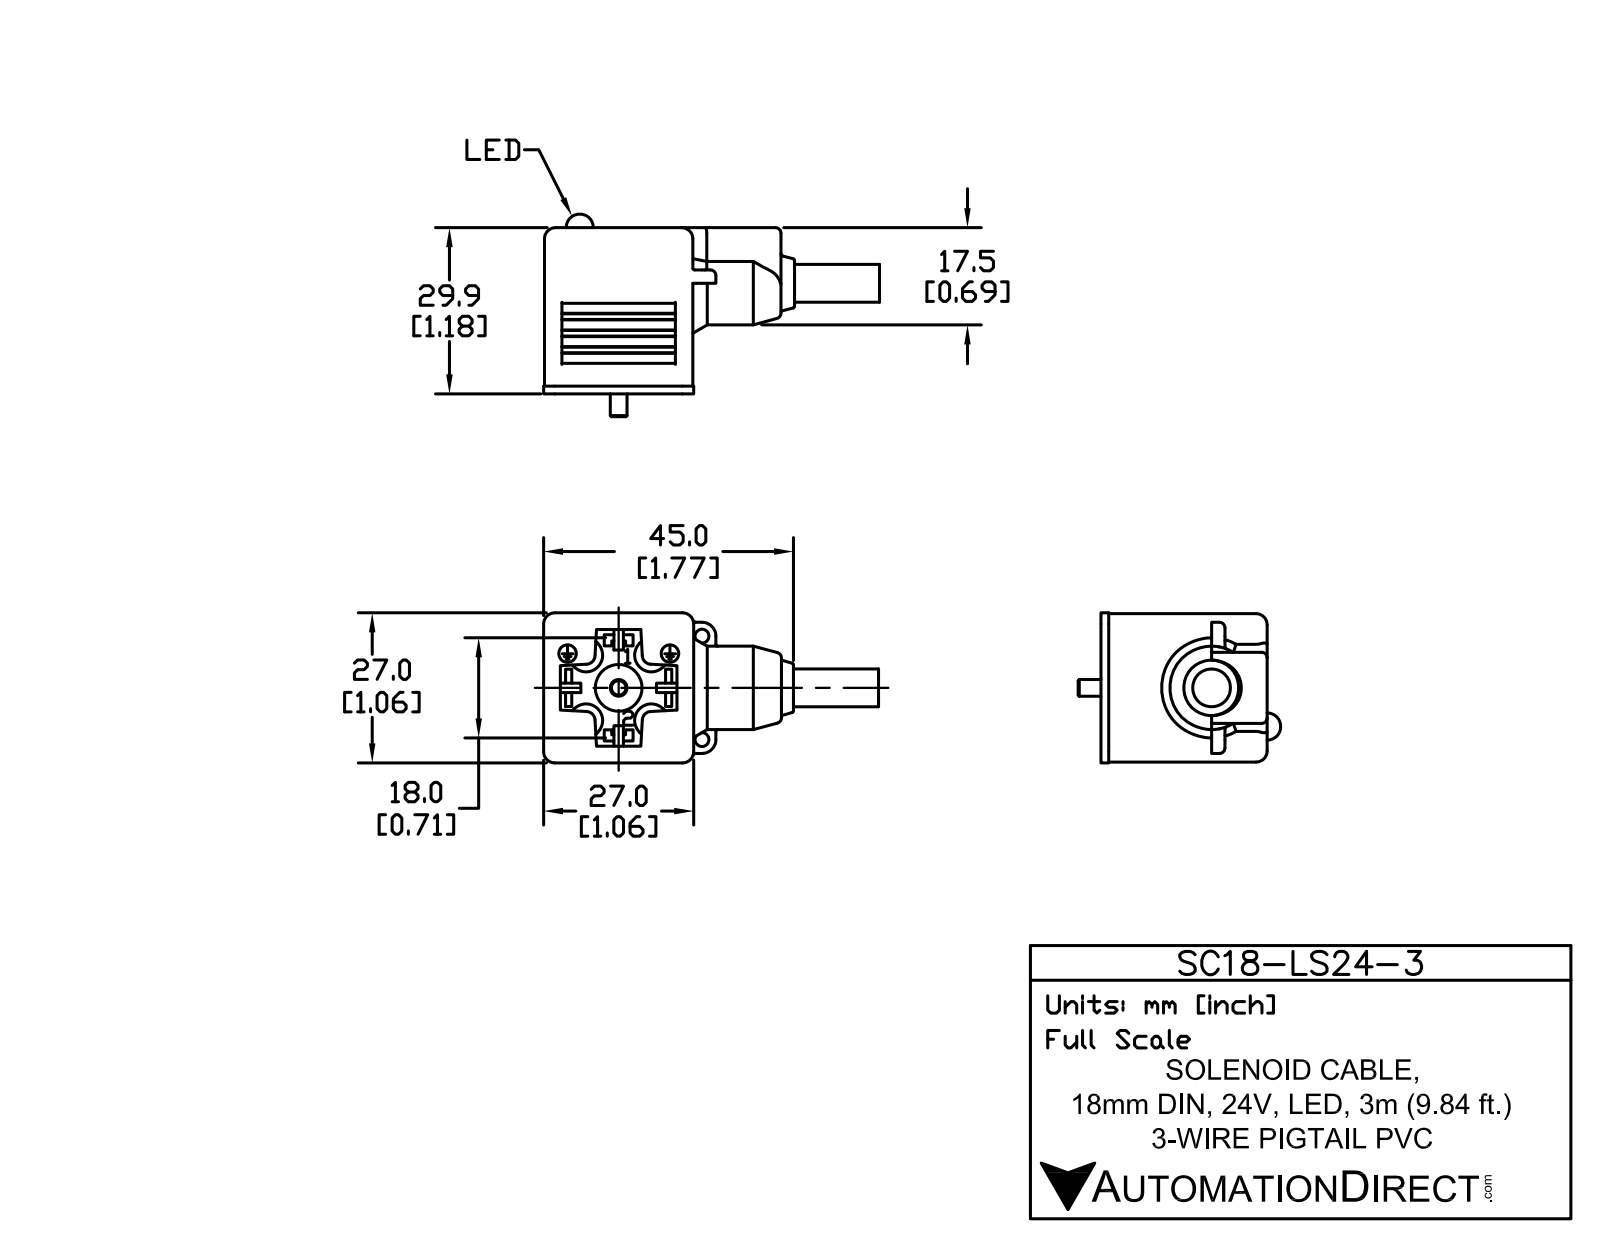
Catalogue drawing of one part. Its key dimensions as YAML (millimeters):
part_name: "SC18-LS24-3"
step_written_by: "SolidWorks 2011 (AUTOMOTIVE_DESIGN)"
units: millimeters
bodies: {solids: 5, faces: 269, planar: 210, cylindrical: 34, other: 25}
overall_size: [73.26, 36.01, 27]
volume: 22295
surface_area: 8255
round_holes:
  - {diameter: 2.25, count: 2}
  - {diameter: 6, count: 2}
  - {diameter: 4, count: 1}
  - {diameter: 8.4, count: 1}
round_bosses_or_shafts:
  - {diameter: 5.75, count: 1}
  - {diameter: 3, count: 1}
  - {diameter: 2.75, count: 1}
partial_cylinders:
  - {radius: 1, count: 11}
  - {radius: 2, count: 4}
  - {radius: 3, count: 4}
  - {radius: 7.5, count: 1}
face_to_face_distances: [23.24, 27, 2, 25.24, 1, 22.24, 24.24, 26.7, 20, 7]
hole_center_spacings: [5.87, 5.9, 11.77]
